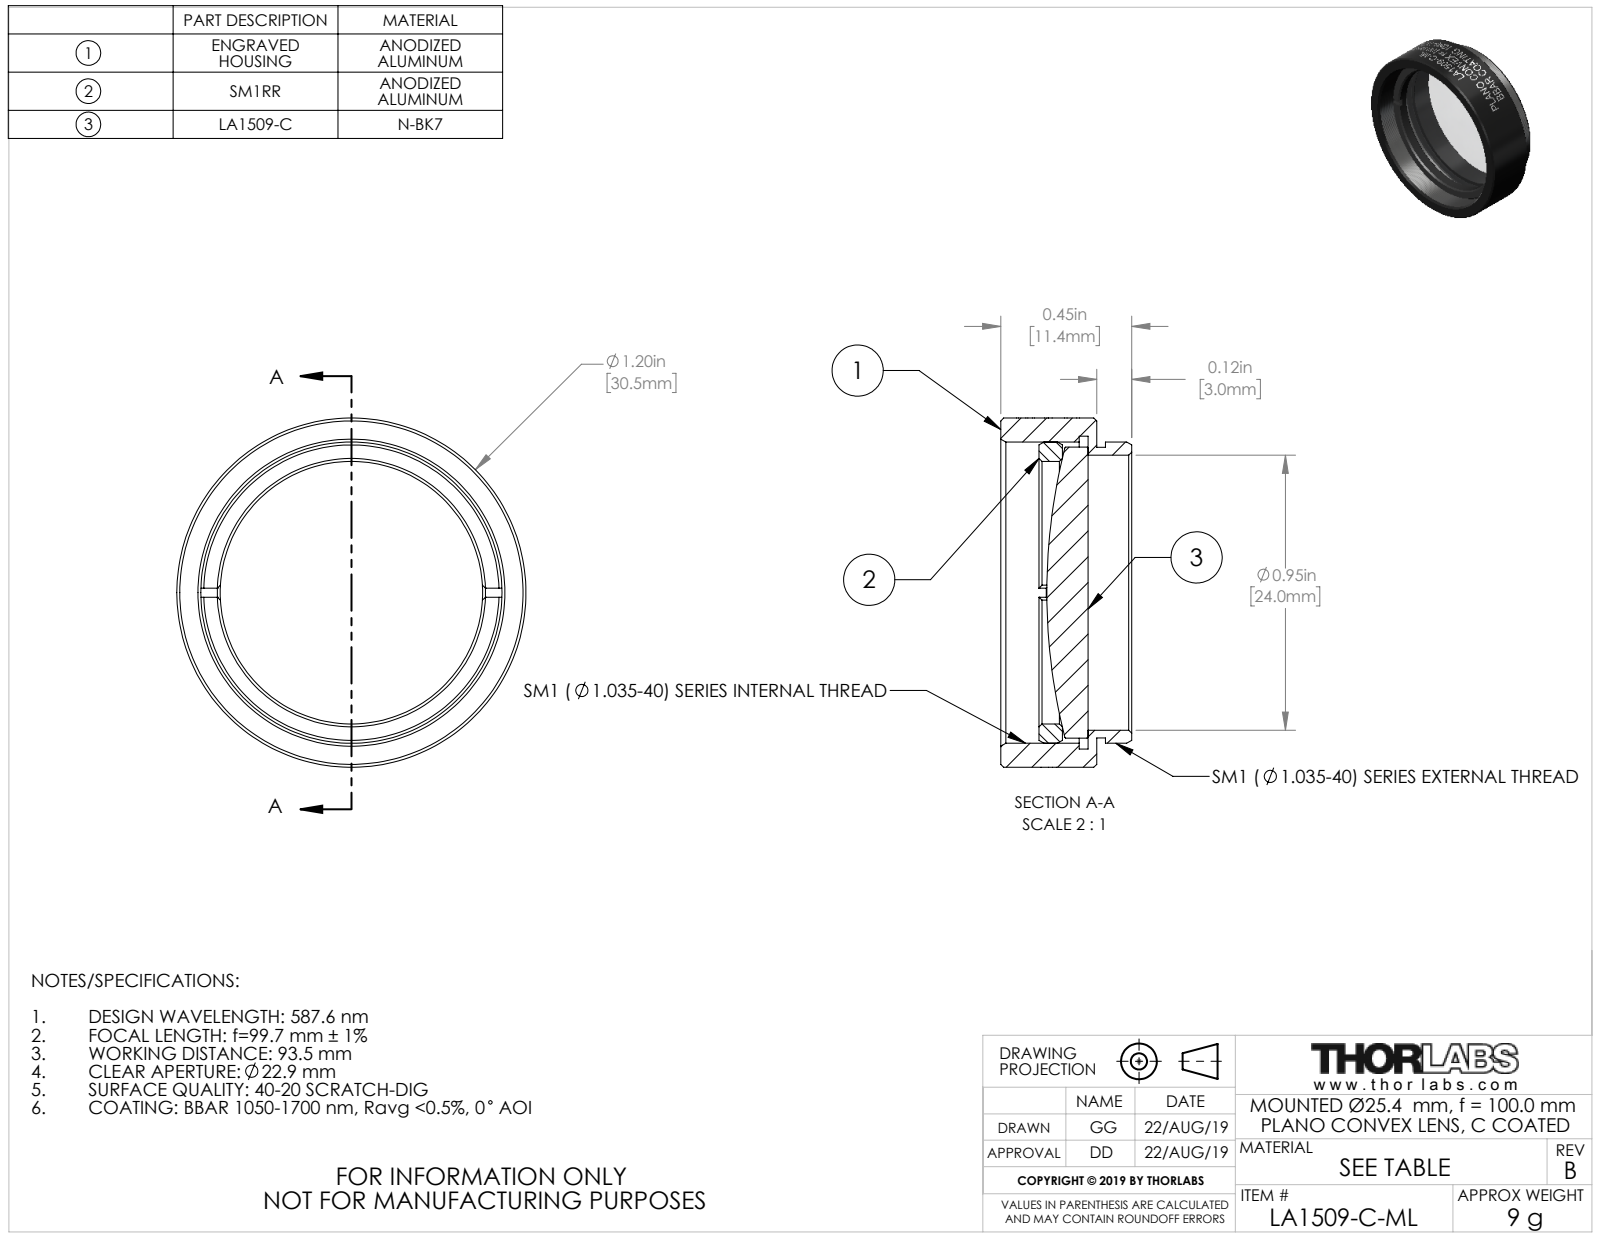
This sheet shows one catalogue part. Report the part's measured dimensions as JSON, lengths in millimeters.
{"part_name": "24413-E0W", "step_written_by": "SolidWorks 2018 (CONFIG_CONTROL_DESIGN)", "units": "millimeters", "bodies": {"solids": 3, "faces": 159, "planar": 20, "cylindrical": 111, "other": 28}, "overall_size": [30.48, 30.48, 11.43], "volume_mm3": 3499, "surface_area_mm2": 4315, "round_holes": [[22.91, 1], [24, 1], [27.3, 1]], "round_bosses_or_shafts": [[30.48, 1], [26.29, 1], [25.4, 1], [25.37, 1]], "face_to_face_distances": [0.76, 8.38, 7.62, 3, 2.24, 5.38, 5.03, 4.27, 2.03, 3.35]}
